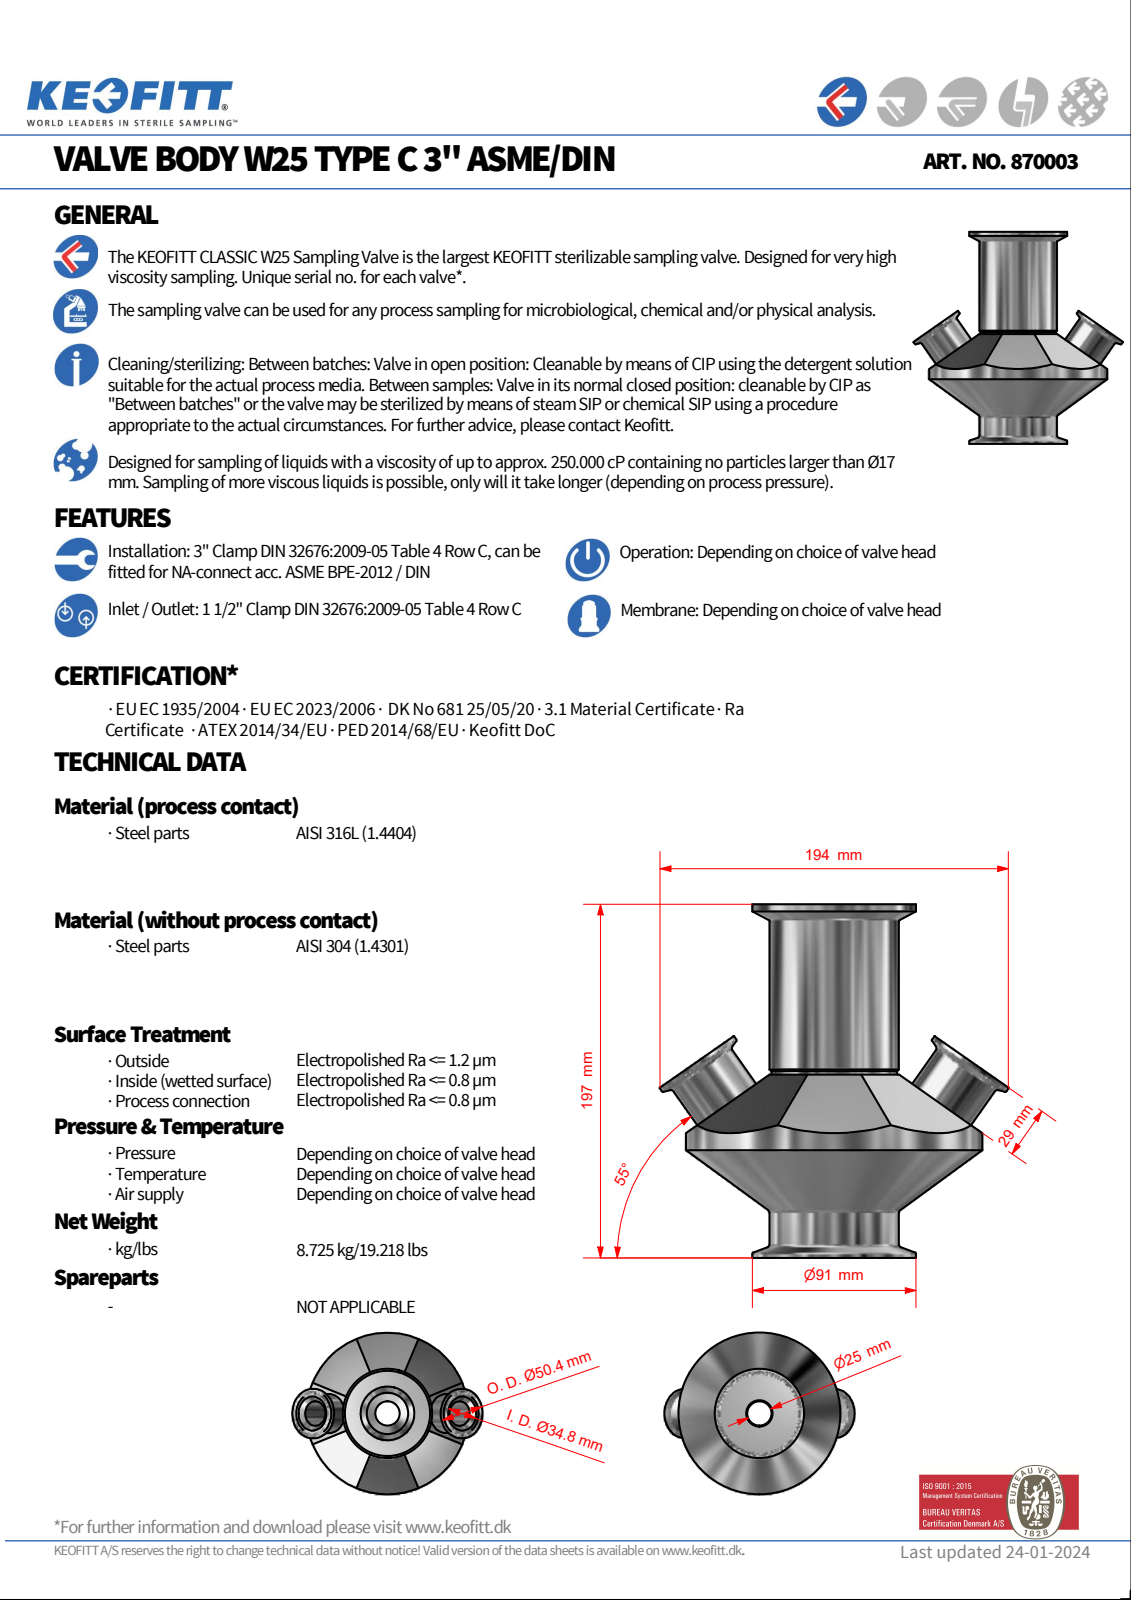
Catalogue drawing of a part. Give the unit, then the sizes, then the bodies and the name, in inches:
Units: inches
Overall size (bounding box): 7.717 × 7.642 × 6.496
Round holes (diameter × count): ⌀0.984 ×3, ⌀2.165 ×1, ⌀3.433 ×1
Round bosses / shafts (diameter × count): ⌀1.984 ×2, ⌀1.575 ×2, ⌀6.496 ×1, ⌀3.583 ×1, ⌀2.835 ×1, ⌀2.756 ×1, ⌀2.565 ×1, ⌀2.559 ×1
Main face-to-face distances: 7.638, 7.459, 0.179, 4.016, 3.443, 3.622, 3.346, 0.669, 4.112, 4.291
Volume: 96.36 in³ · Surface area: 247.6 in²
Bodies: 2 solids, 81 faces (21 planar, 21 cylindrical, 39 other)
Part name (STEP PRODUCT): 870003
STEP written by: Autodesk Inventor 2022 (AUTOMOTIVE_DESIGN)
